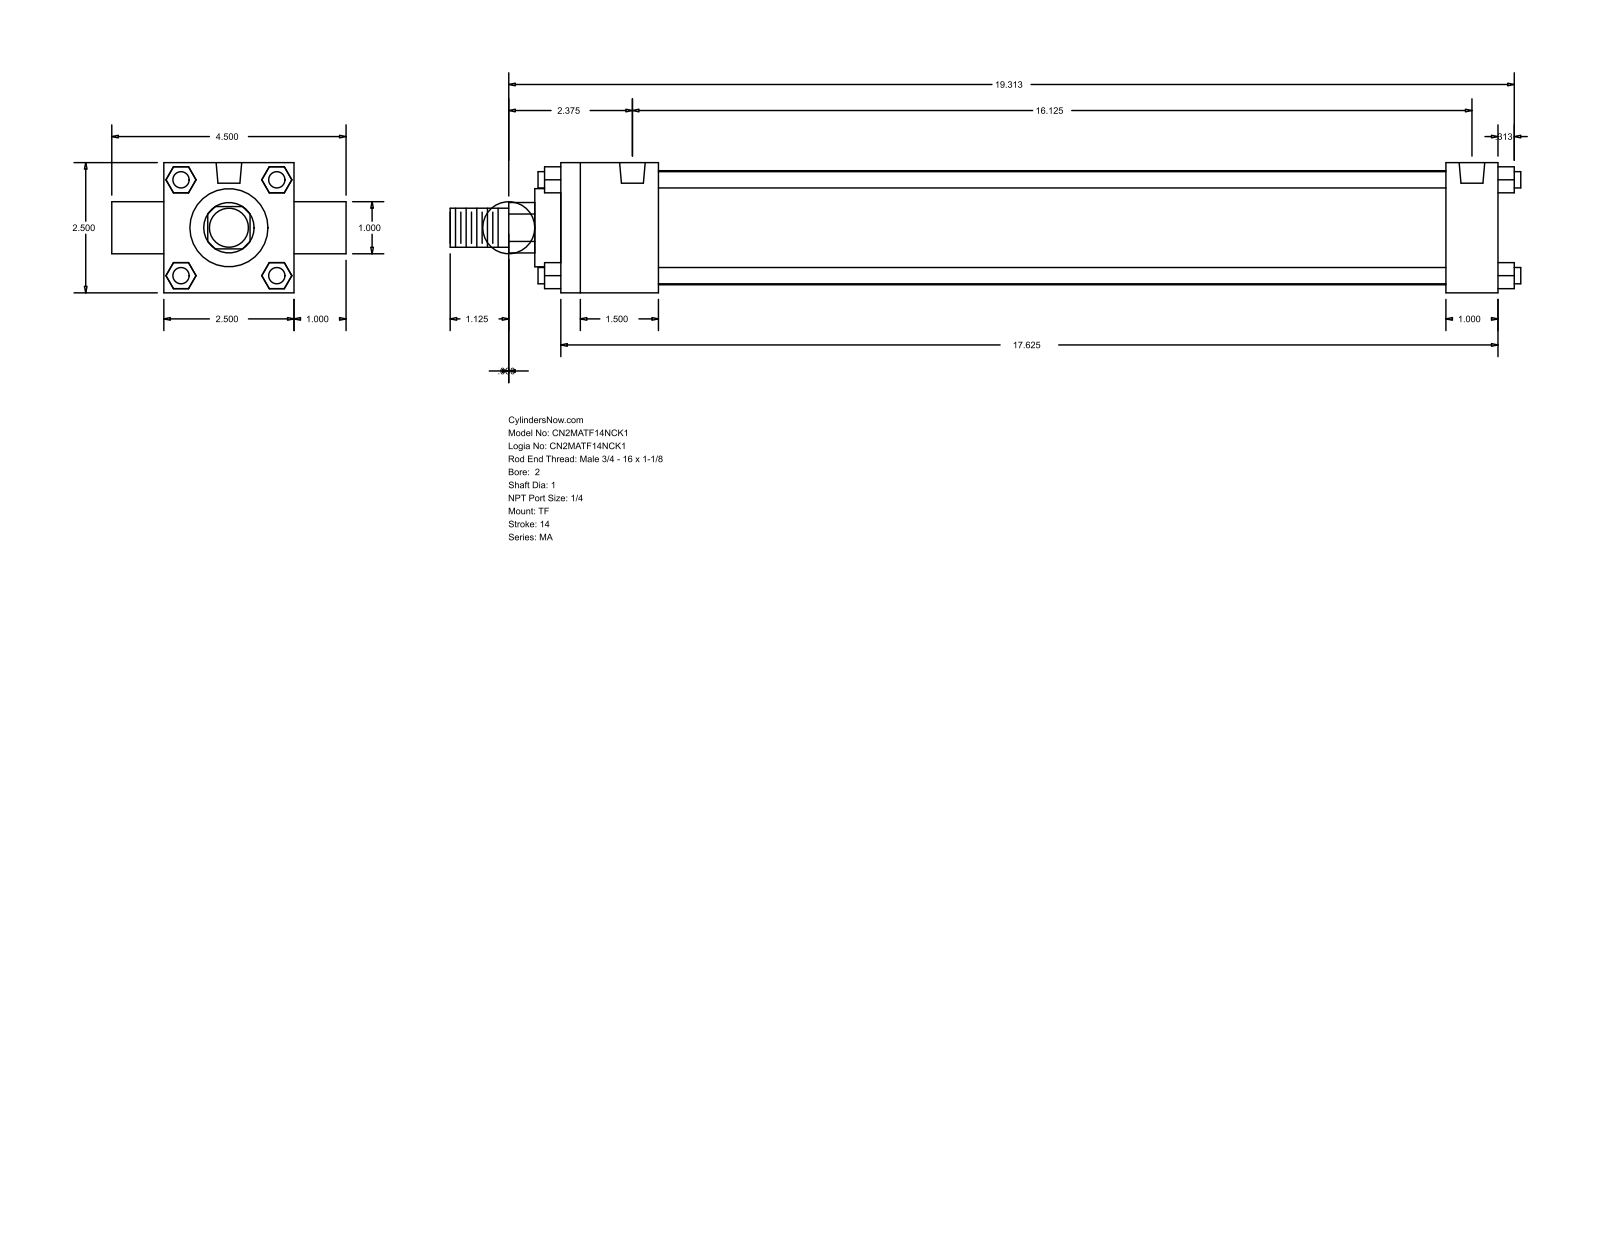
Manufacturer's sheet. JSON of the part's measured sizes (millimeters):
{"part_name": "MA_TF__0200_1", "step_written_by": "GSSL Pune (CONFIG_CONTROL_DESIGN)", "units": "millimeters", "bodies": {"solids": 0, "faces": 120, "planar": 92, "cylindrical": 28, "other": 0}, "overall_size": [522.29, 114.3, 63.5], "round_holes": [[7.94, 3], [12.49, 2]], "round_bosses_or_shafts": [[7.94, 4], [25.4, 2], [55.63, 1], [38.1, 1], [19.05, 1]], "partial_cylinders_radius": [[12.29, 1]], "face_to_face_distances": [63.5, 25.4, 457.2, 12.7, 47.63, 431.8, 384.17, 409.57, 88.9, 23.37], "hole_center_spacings": [409.57]}
